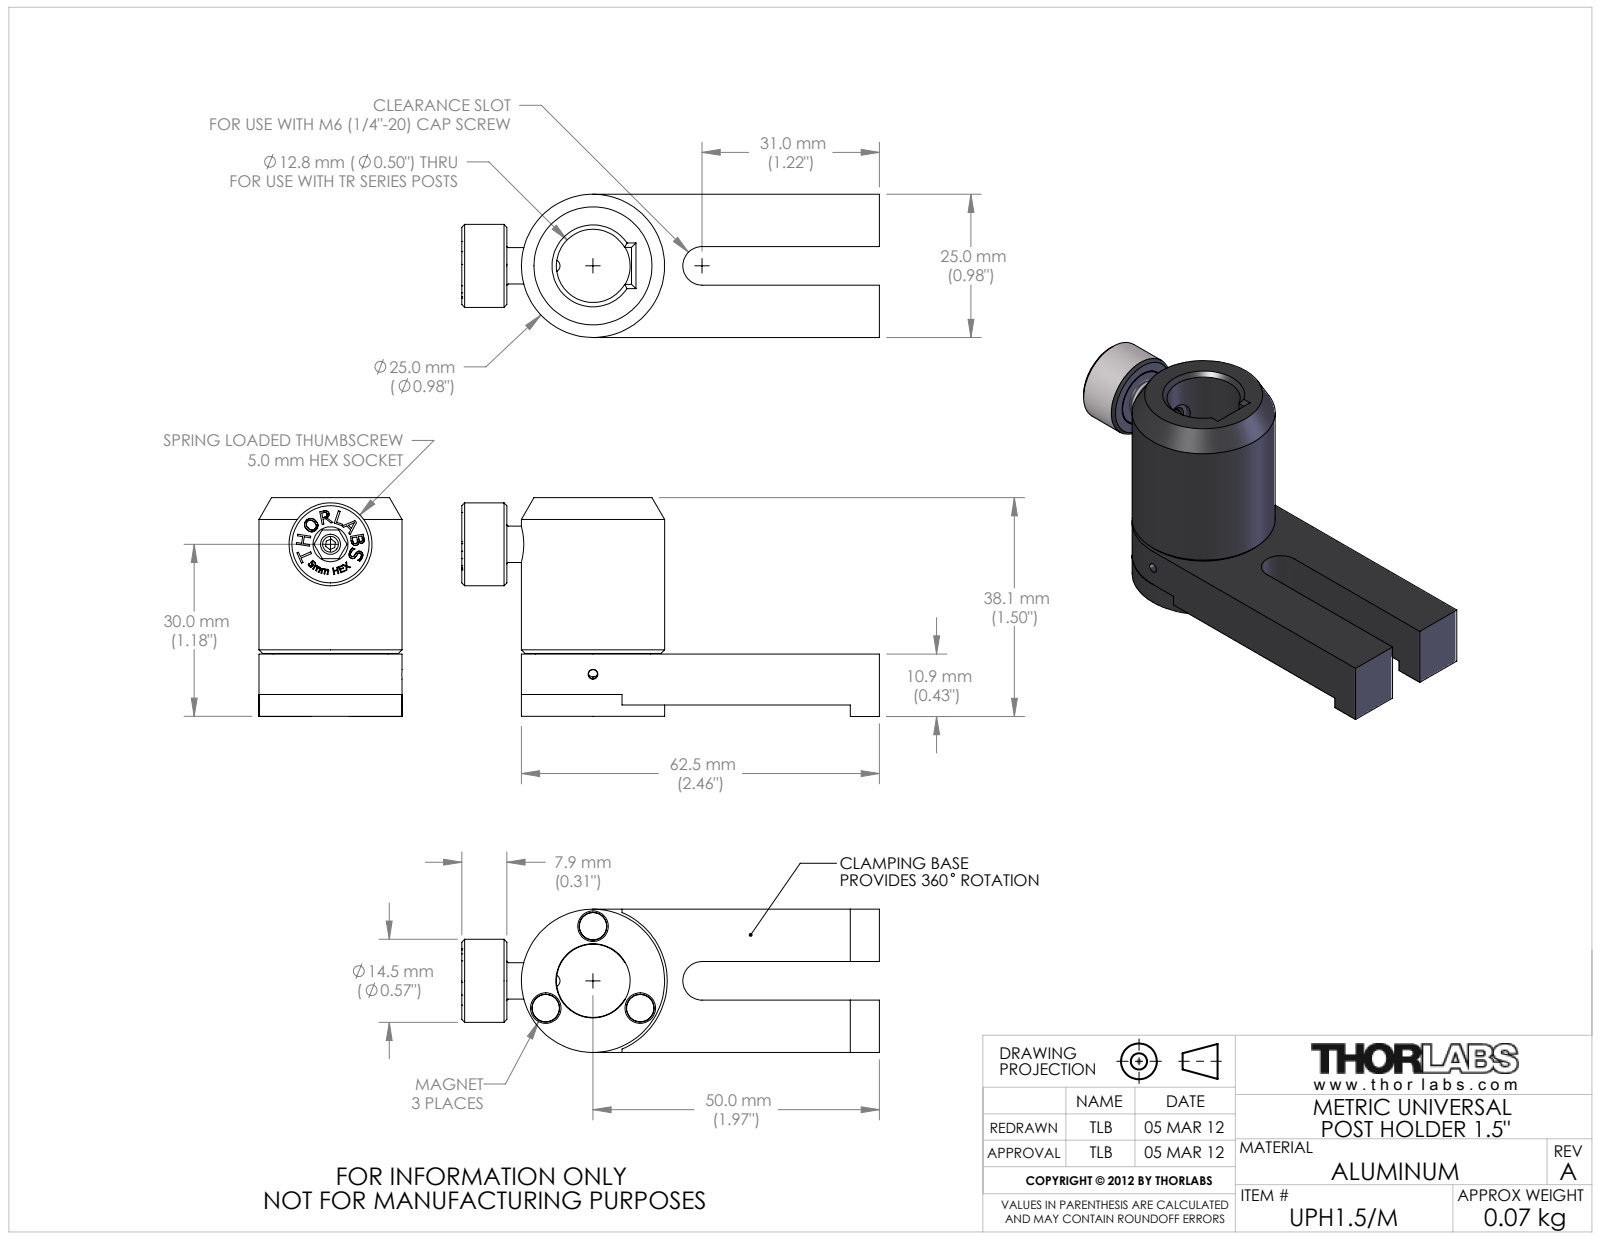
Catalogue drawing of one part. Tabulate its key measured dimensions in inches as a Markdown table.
| quantity | value |
| --- | --- |
| part name | 21063-E0W |
| STEP written by | SolidWorks 2011 (AUTOMOTIVE_DESIGN) |
| units | inches |
| bodies | 10 solids, 436 faces (211 planar, 84 cylindrical, 141 other) |
| overall size | 2.871 × 1.504 × 0.984 |
| volume | 1.312 in³ |
| surface area | 19.5 in² |
| round holes (diameter × count) | 0.19 × 3, 0.063 × 1, 0.067 × 1, 0.07 × 1, 0.084 × 1, 0.1 × 1, 0.125 × 1, 0.138 × 1, 0.201 × 1, 0.4 × 1, 0.503 × 1, 0.51 × 1 |
| round bosses / shafts (diameter × count) | 0.187 × 3, 0.984 × 1, 0.79 × 1, 0.7 × 1, 0.68 × 1, 0.57 × 1, 0.39 × 1, 0.25 × 1 |
| partial cylindrical surfaces (radius × count) | 0.133 × 1, 0.51 × 1 |
| main face-to-face distances | 0.35, 0.359, 0.625, 0.984, 0.072, 0.278, 0.078, 0.15, 0.428, 0.265 |
| hole center spacings | 0.375, 0.65, 0.016, 0.375, 0.649 |
